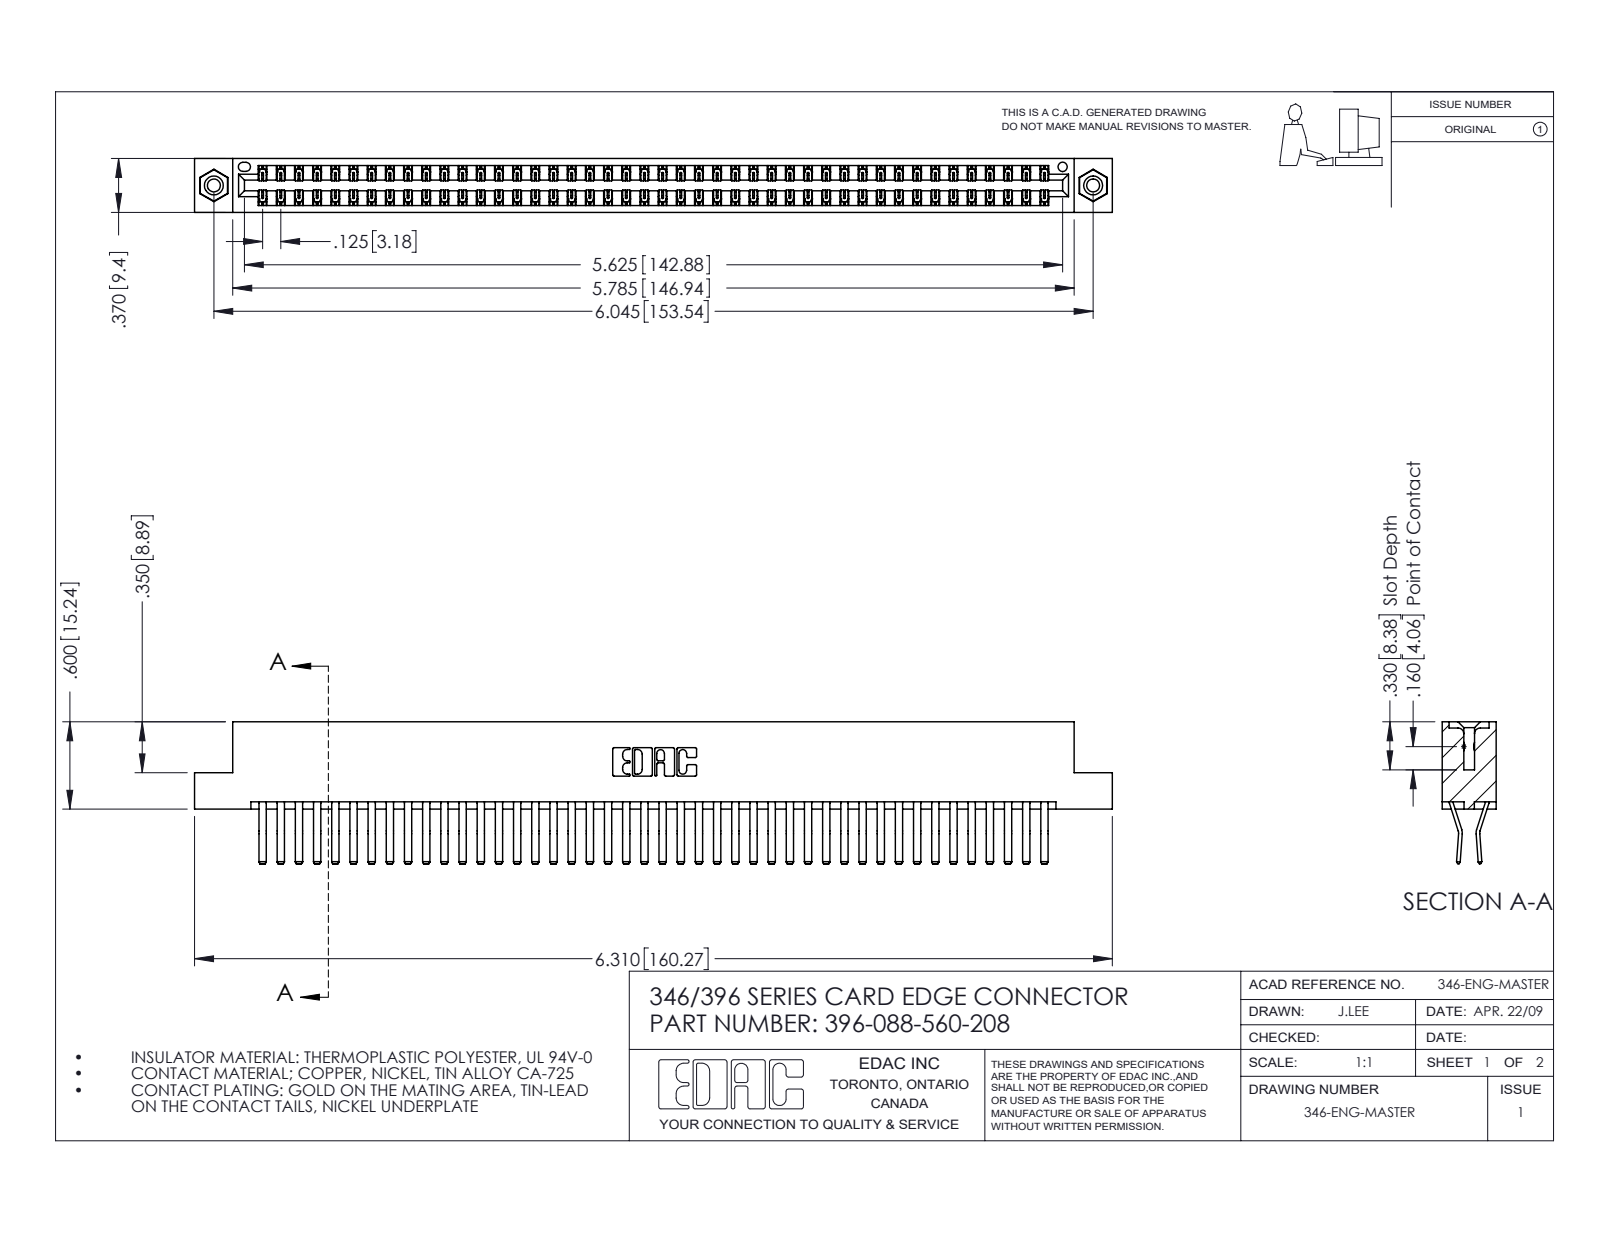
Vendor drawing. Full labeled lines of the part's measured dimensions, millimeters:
Part name (STEP PRODUCT): 345-250-001_345-250-003-102; 396-088-560-208; 346 Part_Flush Mounting Lugs - 0.156 Dia-TI; 345-292-001_560 Tail
STEP written by: SolidWorks 2016 (CONFIG_CONTROL_DESIGN)
Units: millimetres
Bodies: 91 solids, 4934 faces (3188 planar, 1730 cylindrical, 16 other)
Overall size (bounding box): 160.3 × 24.8 × 9.4
Volume: 16 200 mm³ · Surface area: 23 880 mm²
Round holes (diameter × count): ⌀2.3 ×2, ⌀3.2 ×2, ⌀4 ×2, ⌀1.6 ×1
Round bosses / shafts (diameter × count): ⌀3.9 ×2
Partial cylindrical surfaces — rounded edges, fillets, slot ends (radius × count): R0.2 ×132, R0.3 ×22, R0.2 ×6, R0.8 ×6, R0.7 ×3, R0.3 ×2, R0.4 ×2, R0.6 ×2
Main face-to-face distances: 1.2, 8.2, 9.4, 0.6, 6.4, 1.8, 7.6, 7, 3.8, 5.6
Hole centre spacings: 6.2, 148.2, 153.5
